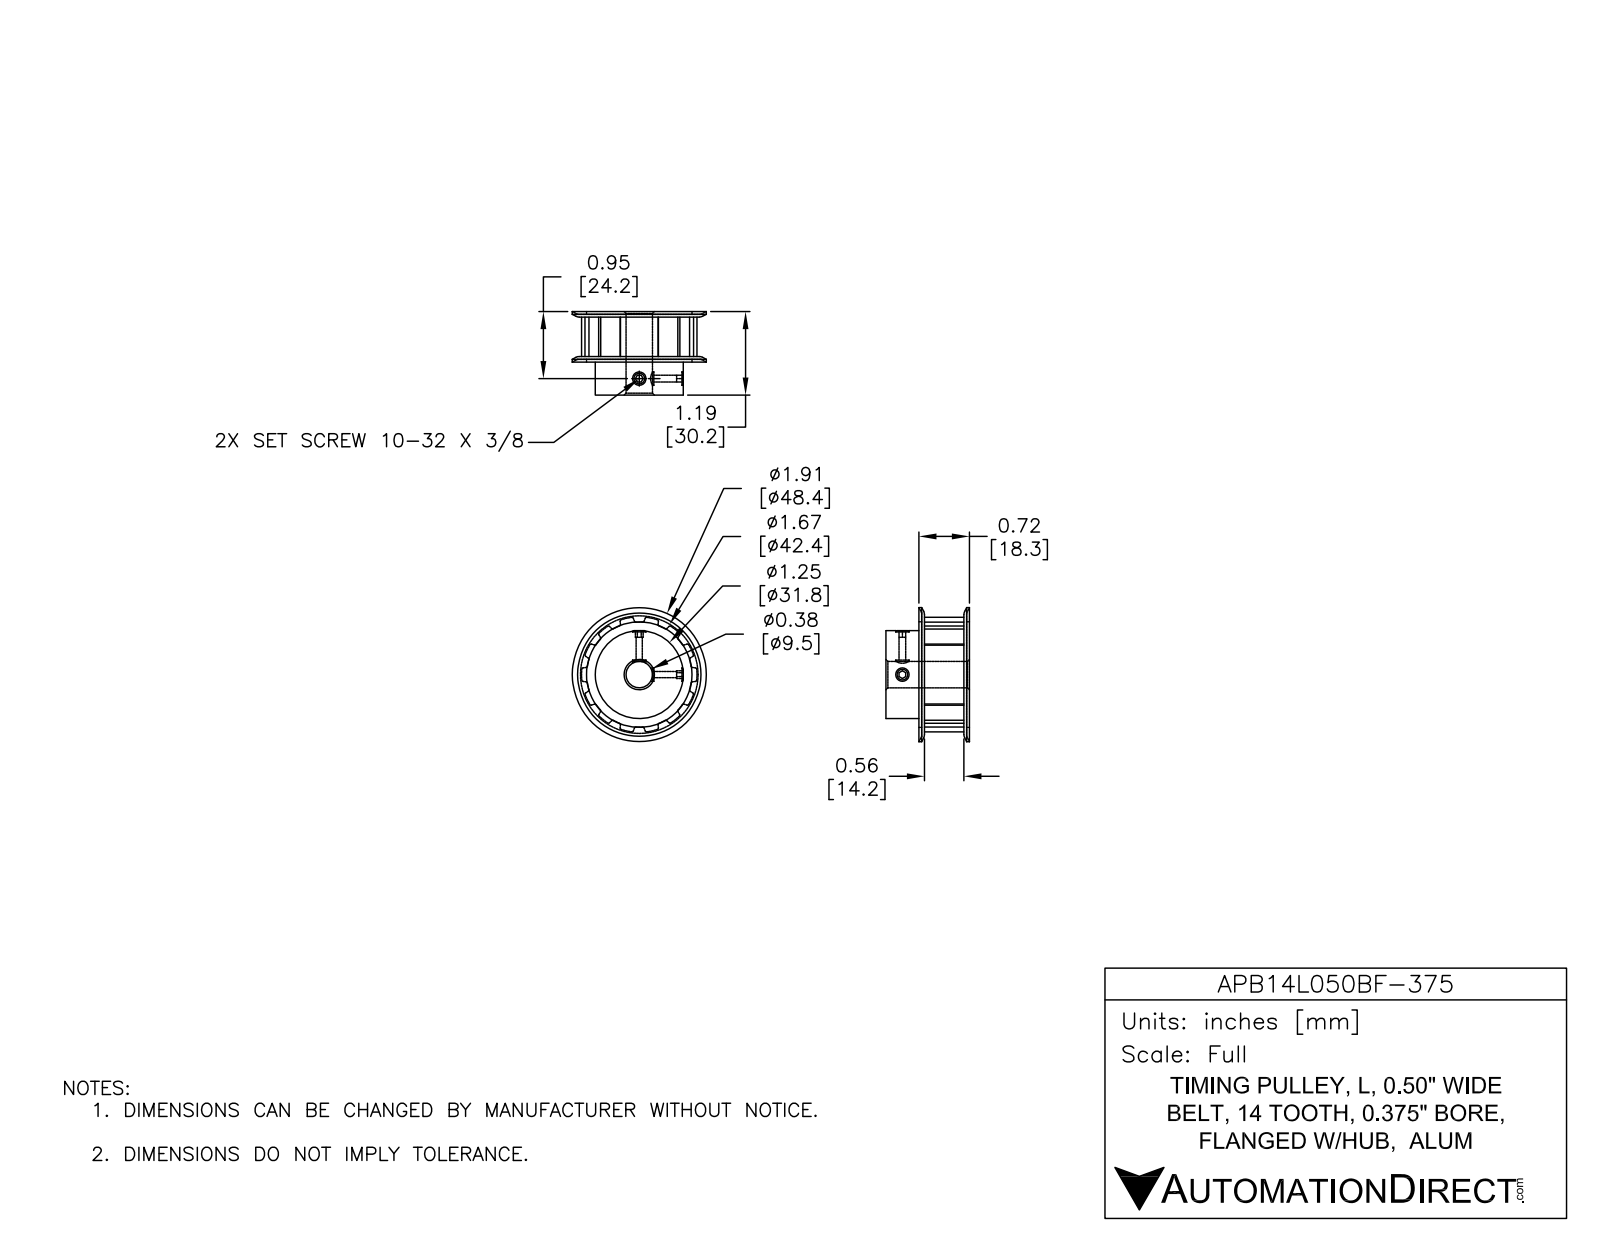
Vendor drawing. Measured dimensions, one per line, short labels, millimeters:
name: APB14L050BF-375
written by: SolidWorks 2014 (AUTOMOTIVE_DESIGN)
unit: mm
bodies: 1 solid, 128 faces (48 planar, 58 cylindrical, 22 other)
size: 48.4 × 48.4 × 30.2
volume: 31 530 mm³; area: 9 484 mm²
holes: 2× ⌀2.2, 1× ⌀9.5
bosses: 1× ⌀31.8
rounds: 28× R0.4, 1× R19.5
face distances: 41.7, 30.2, 17.3, 12.9, 1, 16.3, 29.2, 15.4, 1, 15.2
